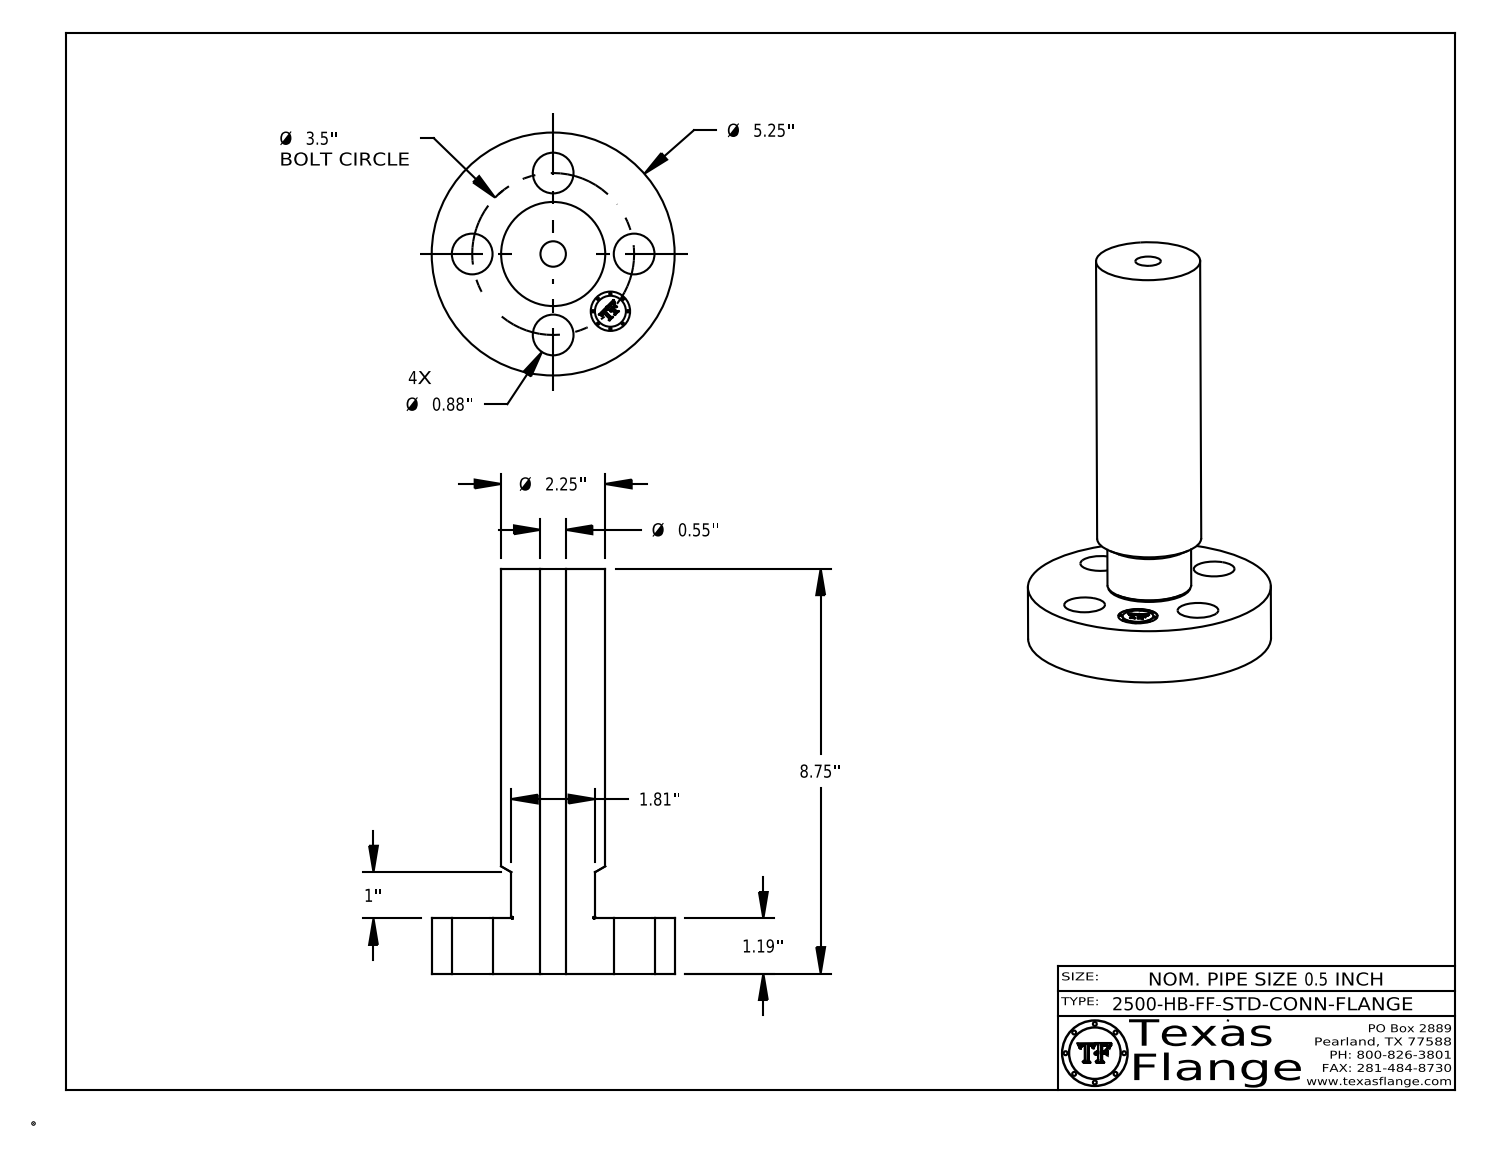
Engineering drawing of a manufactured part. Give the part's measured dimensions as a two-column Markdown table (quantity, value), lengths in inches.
| quantity | value |
| --- | --- |
| part name | 0.5-2500-HB-FF-STD-CONN-FLANGE |
| STEP written by | CATIA V5 STEP AP214 (AUTOMOTIVE_DESIGN) |
| units | inches |
| bodies | 1 solid, 410 faces (368 planar, 36 cylindrical, 6 other) |
| overall size | 8.75 × 5.25 × 5.25 |
| volume | 49.34 in³ |
| surface area | 140.3 in² |
| round holes (diameter × count) | 0.88 × 4, 0.55 × 1, 0.85 × 1 |
| round bosses / shafts (diameter × count) | 0.051 × 8, 5.25 × 1, 2.25 × 1, 1.81 × 1, 0.67 × 1 |
| main face-to-face distances | 1.19, 8.75, 7.56, 1.185, 7.565, 0.016, 0.254, 0.249, 0.046, 0.165 |
| hole center spacings | 1.75, 2.475, 1.339, 3.233, 3.5 |
